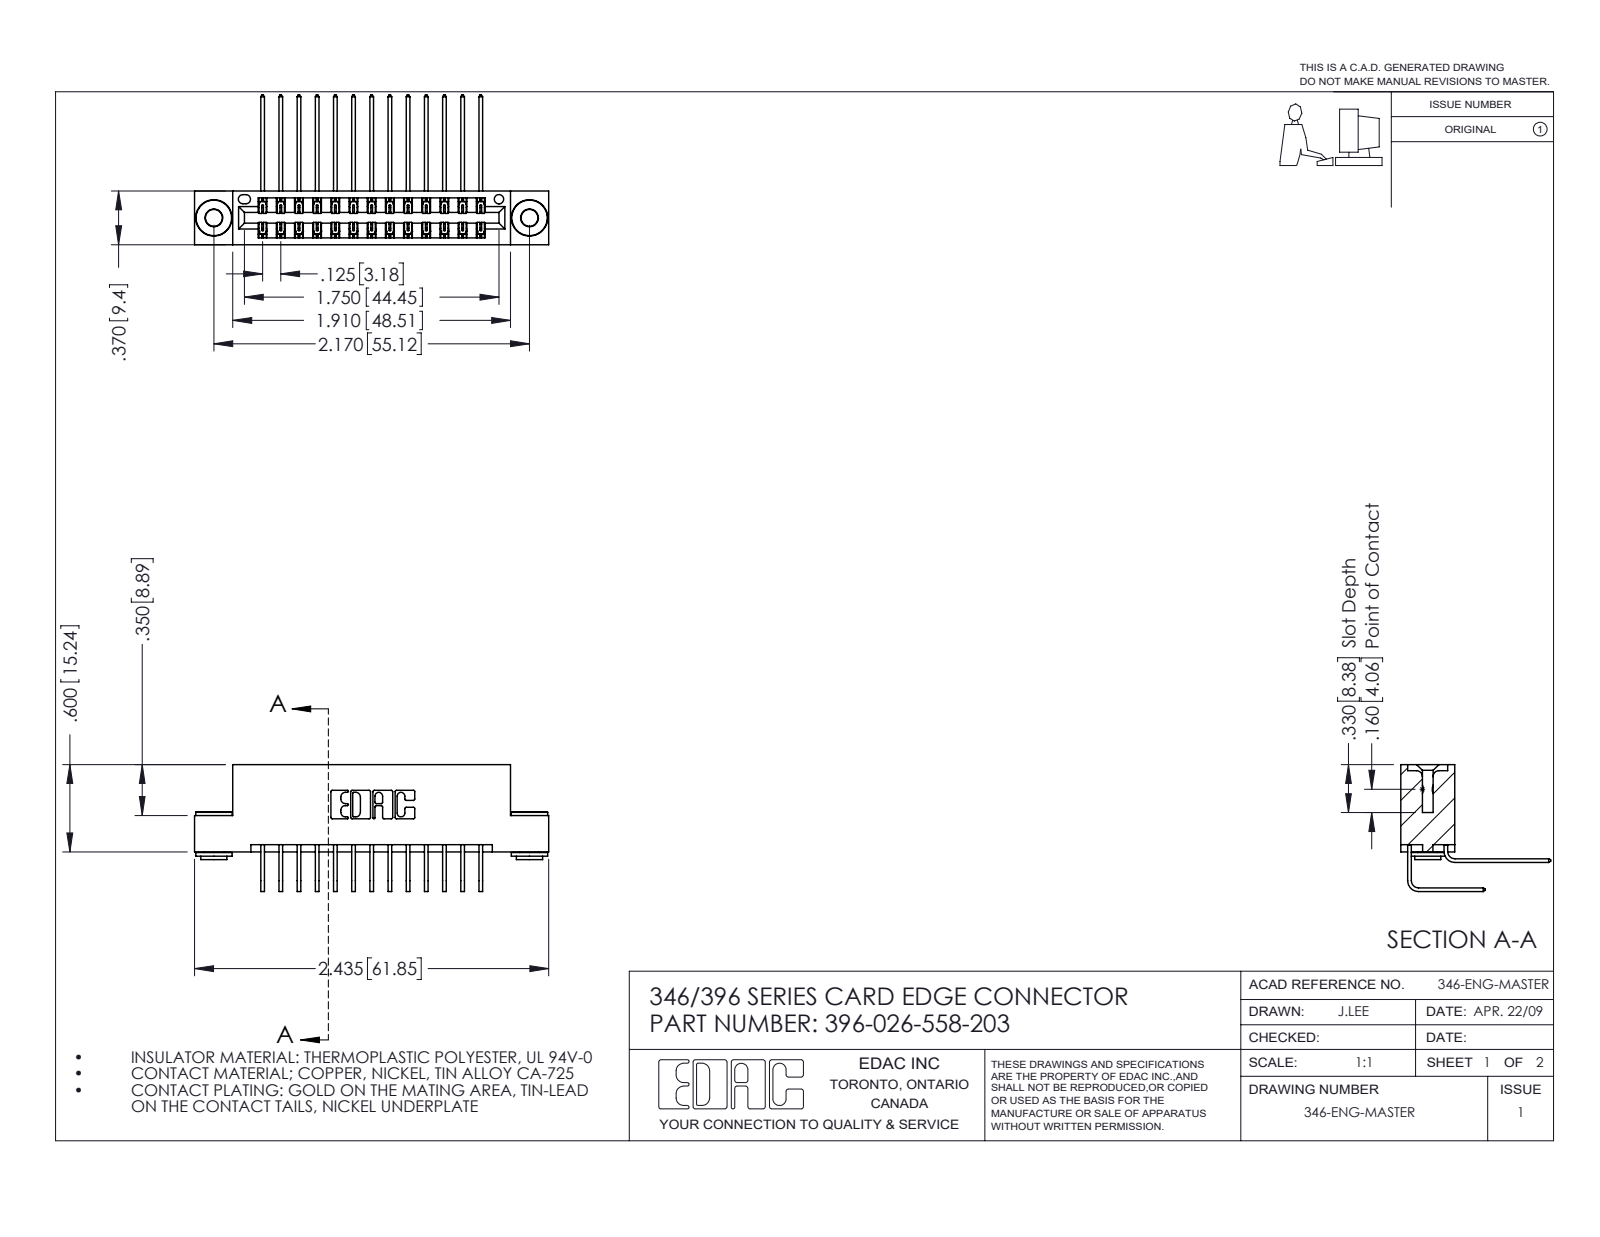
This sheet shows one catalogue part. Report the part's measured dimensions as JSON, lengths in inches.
{"part_name": "345-292-001_558 559 Tail - 1; 345-292-001_558 Tail - 2; 346 Part_Flush Mounting Lugs - 0.156 Dia-TH; 396-026-558-203 (+1 more)", "step_written_by": "SolidWorks 2016 (CONFIG_CONTROL_DESIGN)", "units": "inches", "bodies": {"solids": 29, "faces": 1564, "planar": 1048, "cylindrical": 508, "other": 8}, "overall_size": [2.435, 1.03, 0.873], "volume_in3": 0.365, "surface_area_in2": 13.47, "round_holes": [[0.116, 2], [0.156, 2], [0.064, 1]], "round_bosses_or_shafts": [[0.25, 2], [0.18, 2], [0.136, 2]], "partial_cylinders_radius": [[0.006, 39], [0.01, 22], [0.007, 6], [0.031, 6], [0.026, 3], [0.014, 2], [0.022, 2], [0.024, 2]], "face_to_face_distances": [0.322, 0.048, 0.25, 0.025, 0.37, 0.298, 0.072, 0.275, 0.148, 0.222], "hole_center_spacings": [0.246, 1.964, 2.17]}
